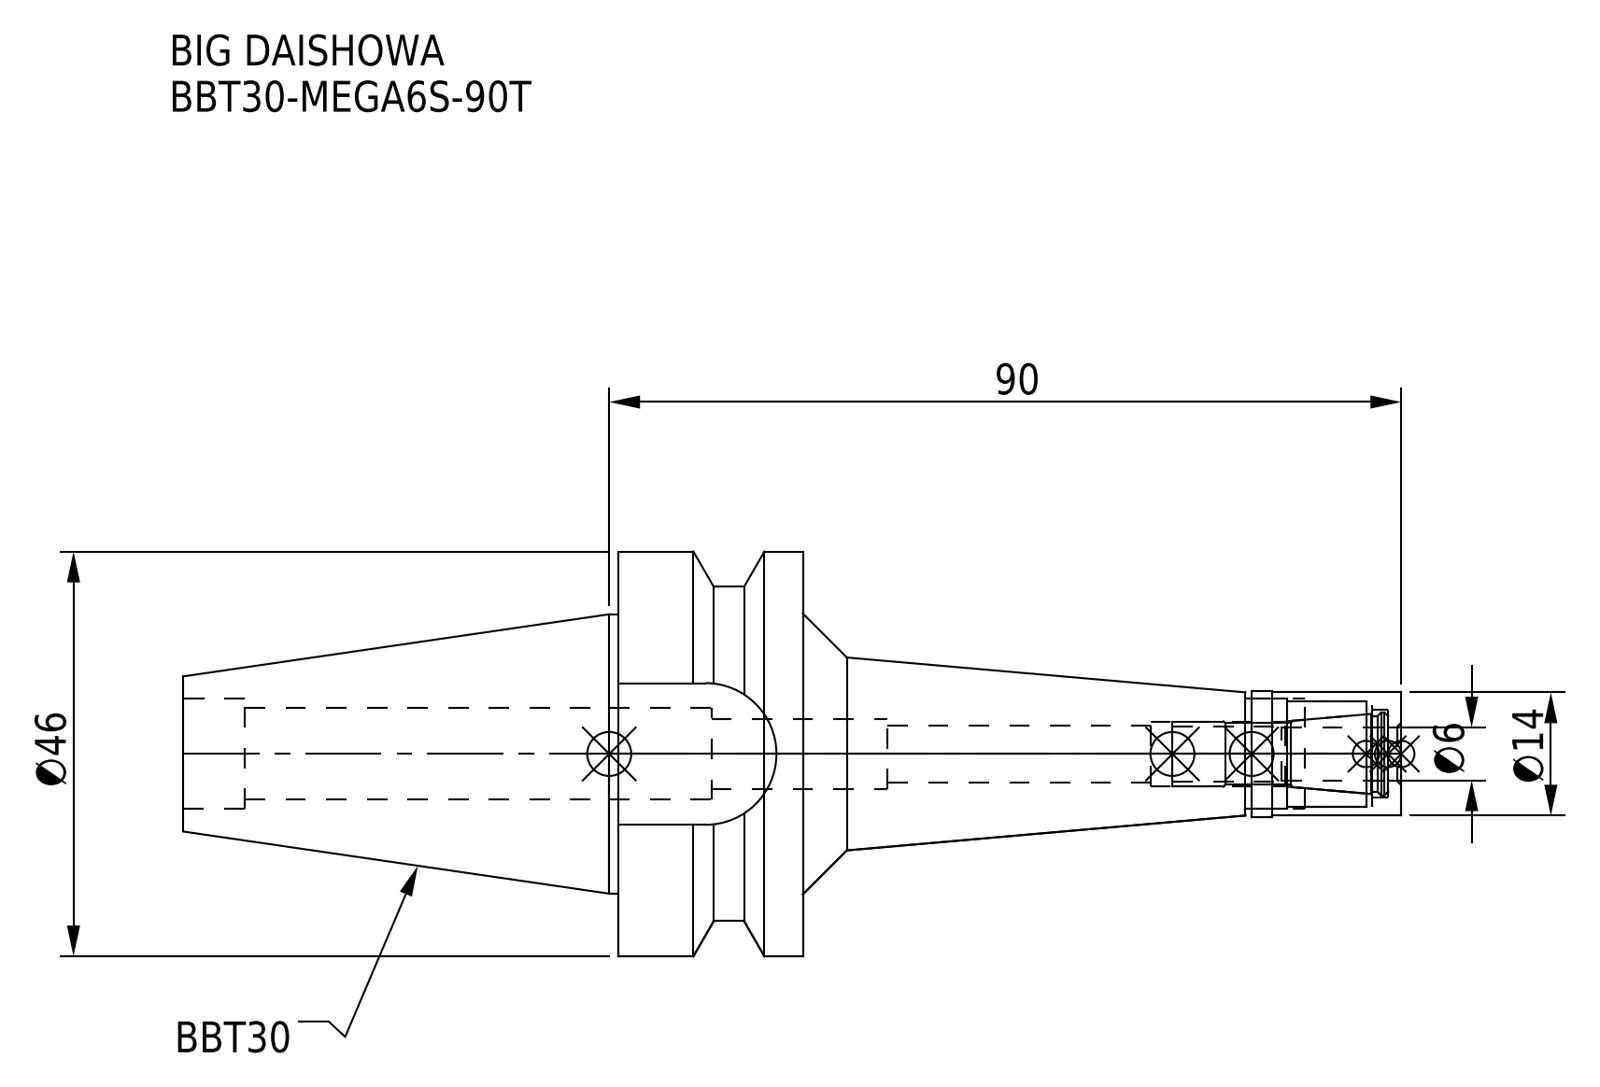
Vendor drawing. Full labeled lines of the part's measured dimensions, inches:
Part name (STEP PRODUCT): DXF_TEMP_ASSY_ASM_4_ASM.stp; BBT30-MEGA6S-90T; MGN6S_1.stp; BBT30-MEGA6S-90T_1.stp (+3 more)
STEP written by: SolidWorks 2019 (CONFIG_CONTROL_DESIGN)
Units: inches
Bodies: 2 solids, 74 faces (22 planar, 38 cylindrical, 14 other)
Overall size (bounding box): 5.449 × 1.811 × 1.811
Volume: 3.804 in³ · Surface area: 28.69 in²
Round holes (diameter × count): ⌀0.24 ×1, ⌀0.252 ×1, ⌀0.291 ×1, ⌀0.315 ×1, ⌀0.394 ×1, ⌀0.409 ×1, ⌀0.472 ×1, ⌀0.492 ×1
Round bosses / shafts (diameter × count): ⌀1.811 ×1, ⌀1.25 ×1, ⌀0.563 ×1, ⌀0.551 ×1
Partial cylindrical surfaces — rounded edges, fillets, slot ends (radius × count): R0.317 ×1, R0.748 ×1
Main face-to-face distances: 0.827, 1.283, 2.772, 1.945, 2.677, 3.504, 5.449, 0.634, 0.028, 0.539
